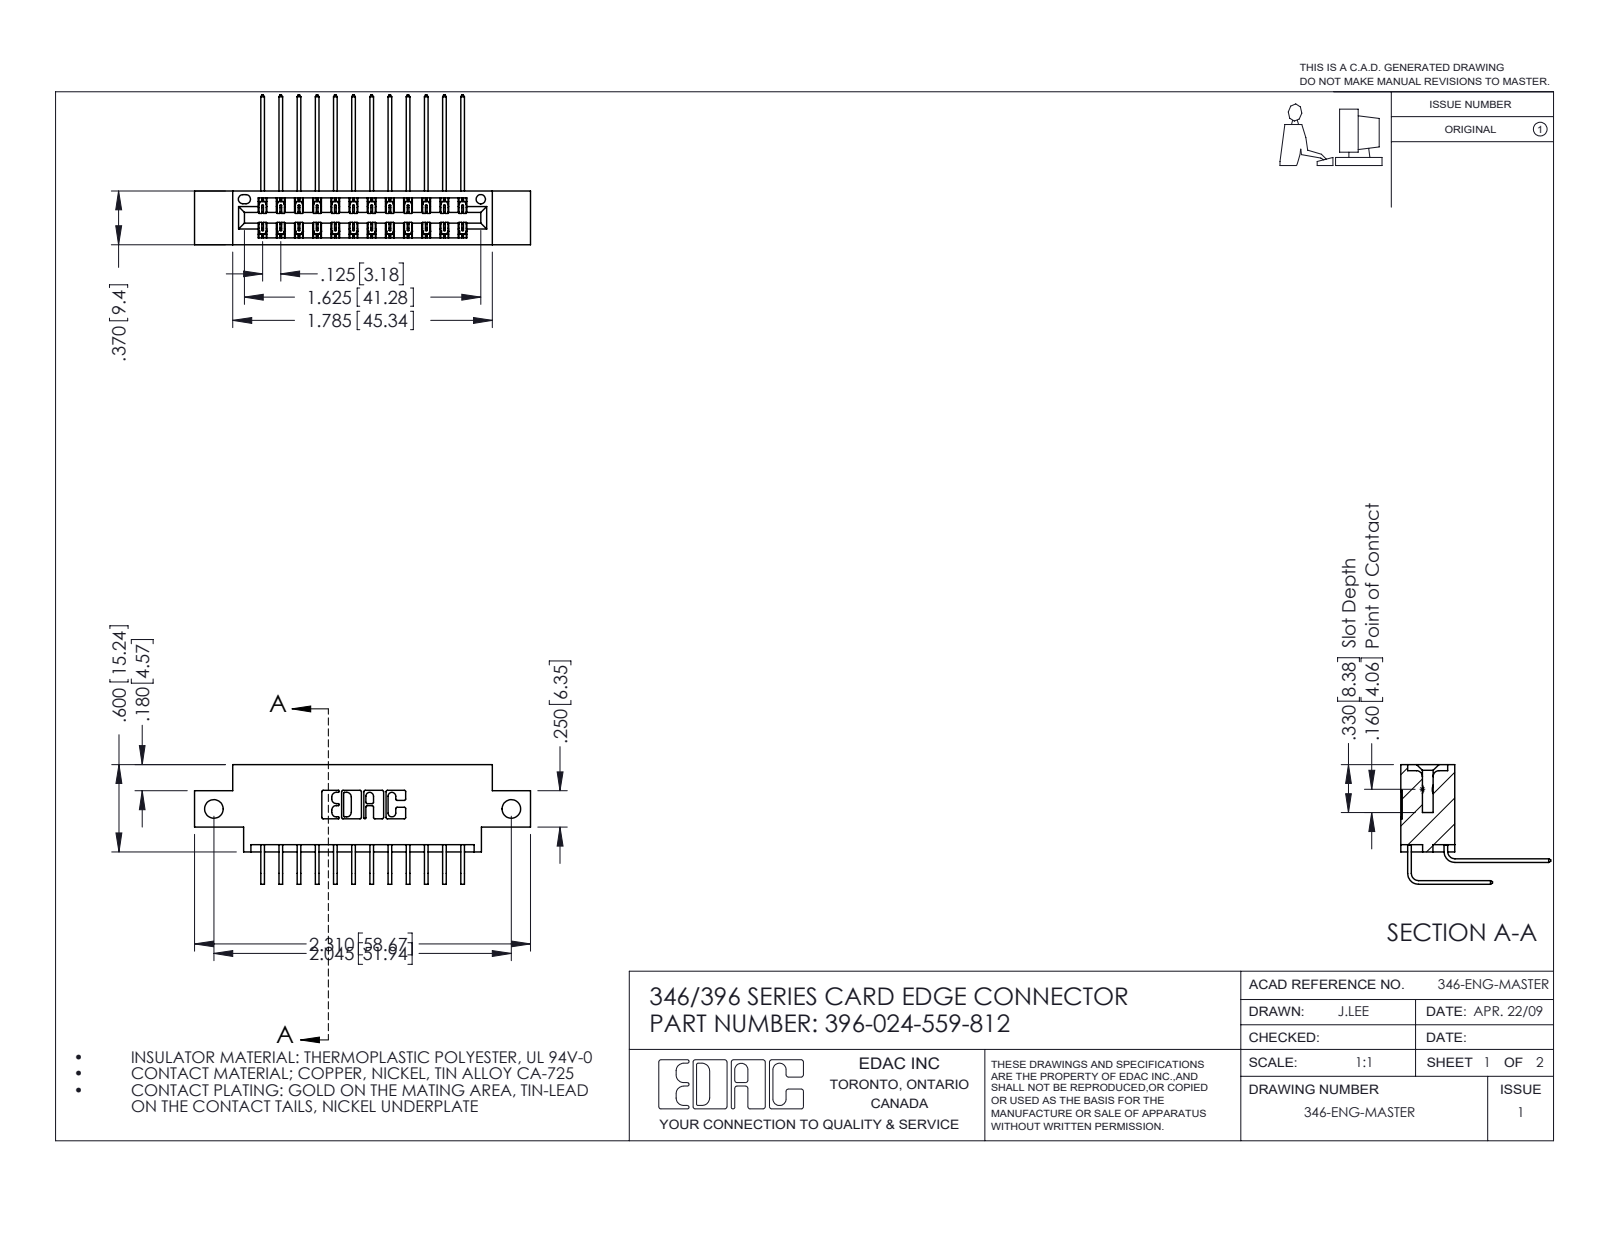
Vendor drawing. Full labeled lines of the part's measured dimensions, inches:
Part name (STEP PRODUCT): 345-292-001_559 Tail - 2; 345-292-001_558 559 Tail - 1; 346 Part_0.170 Offset - Side Mount; 396-024-559-812
STEP written by: SolidWorks 2016 (CONFIG_CONTROL_DESIGN)
Units: inches
Bodies: 25 solids, 1422 faces (968 planar, 454 cylindrical, 0 other)
Overall size (bounding box): 2.31 × 1.03 × 0.823
Volume: 0.329 in³ · Surface area: 11.84 in²
Round holes (diameter × count): ⌀0.128 ×2, ⌀0.064 ×1
Partial cylindrical surfaces — rounded edges, fillets, slot ends (radius × count): R0.006 ×36, R0.01 ×22, R0.007 ×6, R0.031 ×6, R0.026 ×3, R0.014 ×2, R0.022 ×2, R0.024 ×2
Main face-to-face distances: 0.048, 0.25, 0.322, 0.37, 0.025, 0.072, 0.298, 0.275, 0.148, 0.222
Hole centre spacings: 2.045
